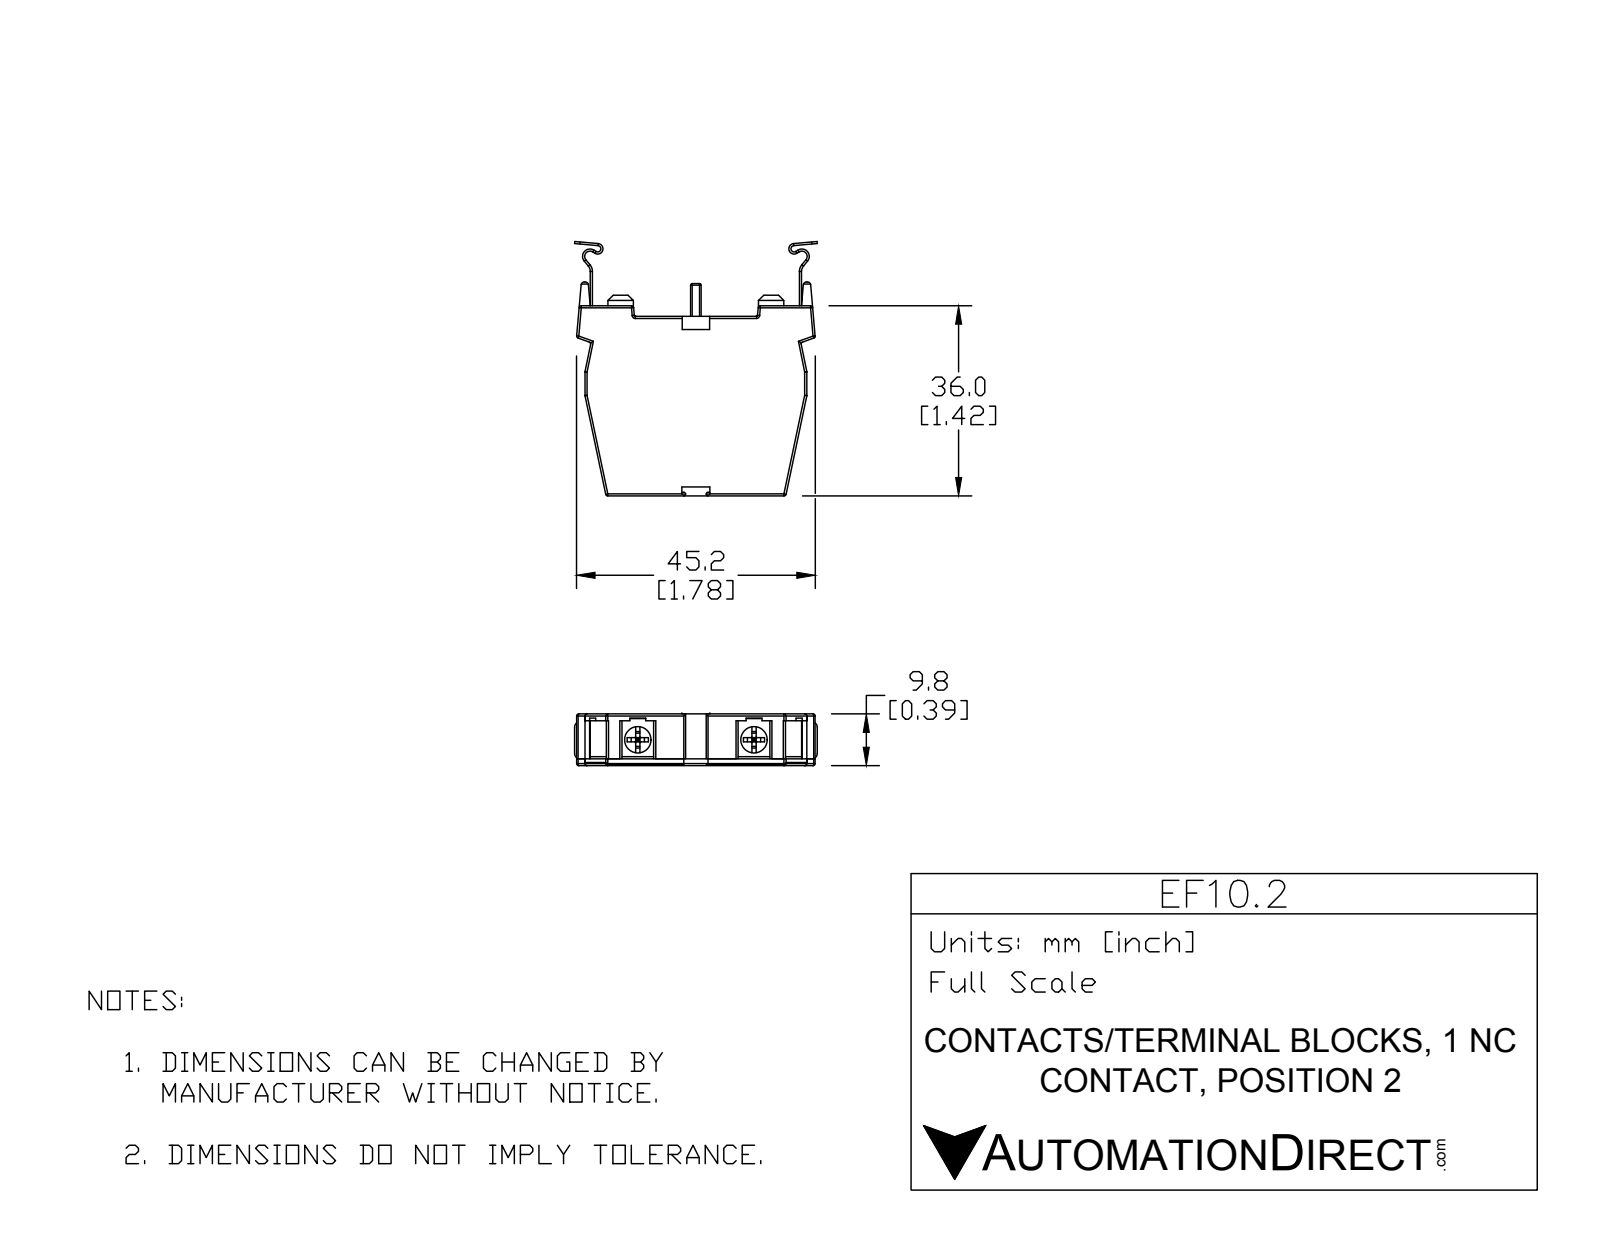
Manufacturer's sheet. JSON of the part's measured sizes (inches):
{"part_name": "EF10.2", "step_written_by": "SolidWorks 2016 (AUTOMOTIVE_DESIGN)", "units": "inches", "bodies": {"solids": 7, "faces": 277, "planar": 155, "cylindrical": 100, "other": 22}, "overall_size": [1.896, 1.822, 0.386], "volume_in3": 0.742, "surface_area_in2": 10.33, "round_holes": [[0.197, 4]], "round_bosses_or_shafts": [[0.187, 2], [0.157, 2]], "partial_cylinders_radius": [[0.01, 44], [0.02, 8], [0.039, 6], [0.024, 4], [0.024, 2], [0.039, 2], [0.055, 2], [0.063, 2]], "face_to_face_distances": [0.386, 0.055, 0.331, 1.339, 0.276, 0.016, 0.079, 0.125, 1.464, 0.138], "hole_center_spacings": [0.859]}
